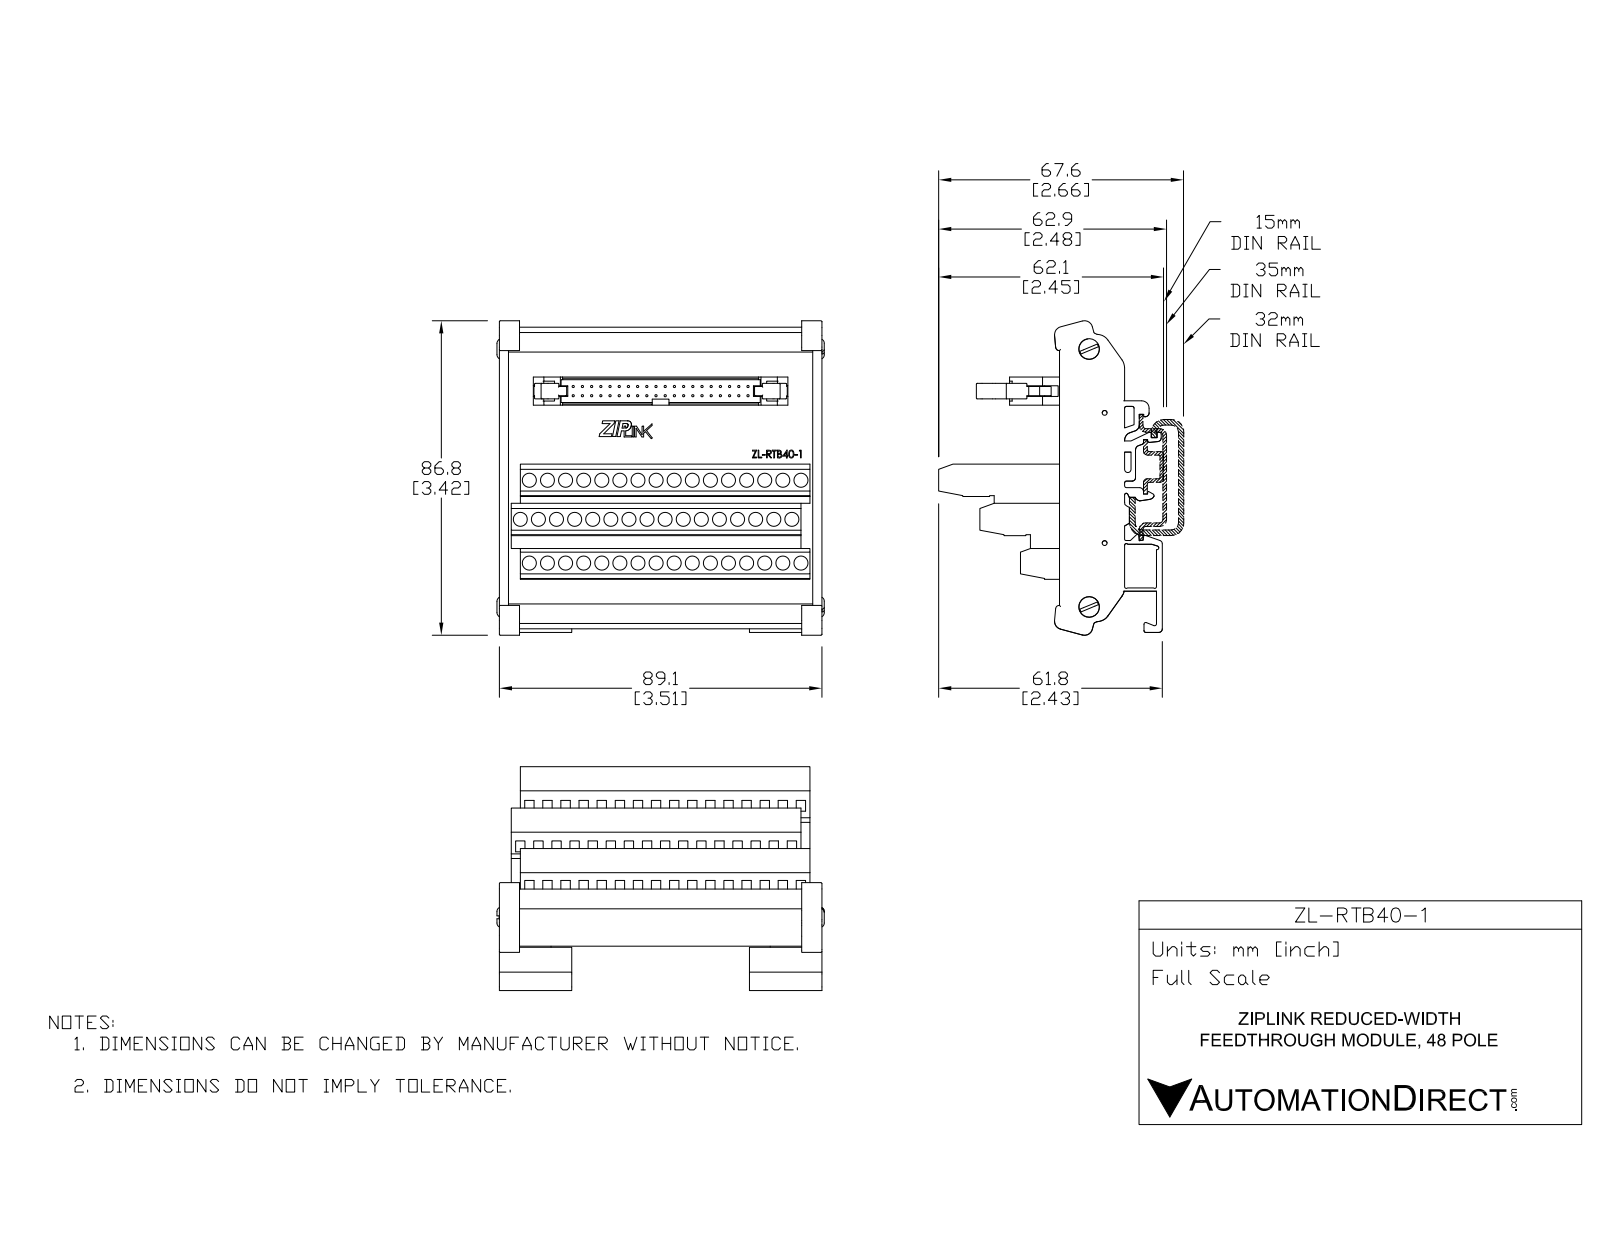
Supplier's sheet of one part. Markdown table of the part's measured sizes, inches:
| quantity | value |
| --- | --- |
| part name | ZL-RTB40-1 |
| STEP written by | SolidWorks 2016 (AUTOMOTIVE_DESIGN) |
| units | inches |
| bodies | 12 solids, 2388 faces (1229 planar, 1043 cylindrical, 116 other) |
| overall size | 3.543 × 3.419 × 2.432 |
| volume | 6.892 in³ |
| surface area | 143.4 in² |
| round holes (diameter × count) | 0.055 × 48, 0.152 × 48, 0.033 × 40, 0.052 × 2, 0.059 × 2, 0.065 × 2, 0.098 × 2, 0.138 × 2, 0.24 × 2 |
| round bosses / shafts (diameter × count) | 0.063 × 48, 0.033 × 40, 0.024 × 40, 0.217 × 2, 0.157 × 2, 0.118 × 2 |
| partial cylindrical surfaces (radius × count) | 0.02 × 62, 0.02 × 52, 0.008 × 47, 0.01 × 24, 0.012 × 10, 0.035 × 5, 0.039 × 5, 0.05 × 5 |
| main face-to-face distances | 0.059, 0.213, 0.06, 0.238, 0.178, 0.272, 0.45, 0.51, 0.237, 0.297 |
| hole center spacings | 0.1, 0.2, 0.3, 0.4, 0.5, 0.141, 0.224, 0.6 |
